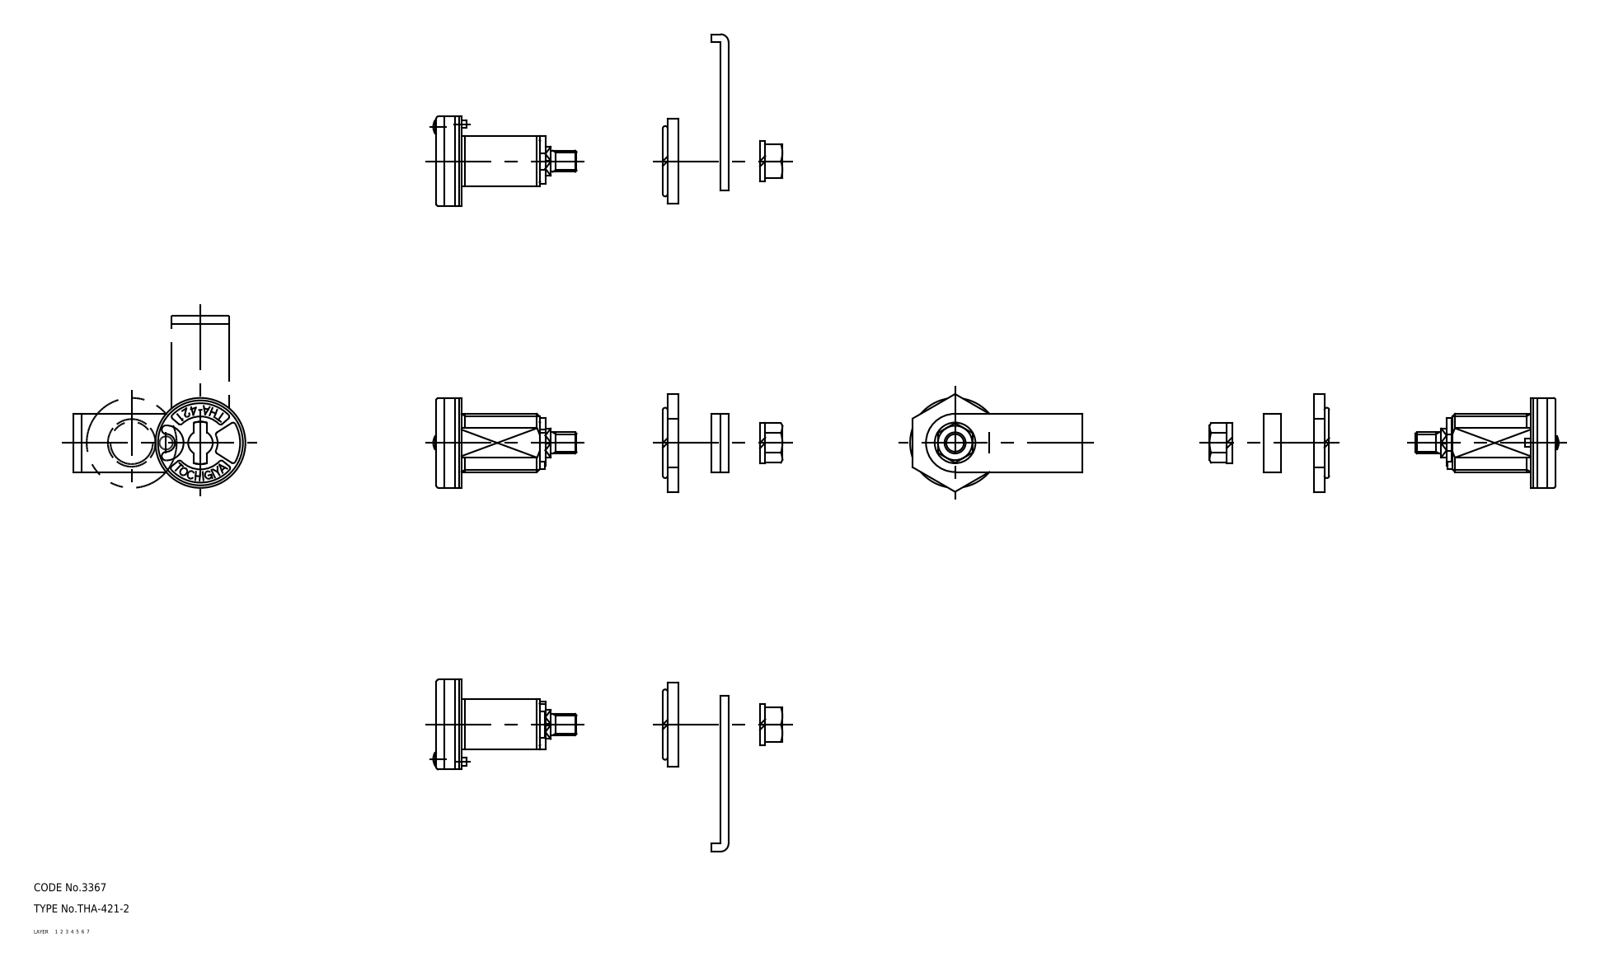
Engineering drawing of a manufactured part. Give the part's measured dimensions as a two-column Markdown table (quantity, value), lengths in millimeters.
| quantity | value |
| --- | --- |
| part name | washer_B; rotor; packing; nut_2 (+6 more) |
| STEP written by | CADfix (AUTOMOTIVE_DESIGN) |
| units | millimeters |
| bodies | 9 solids, 208 faces (0 planar, 0 cylindrical, 208 other) |
| overall size | 66.47 × 54.2 × 34 |
| volume | 24 979 mm³ |
| surface area | 17 423 mm² |
